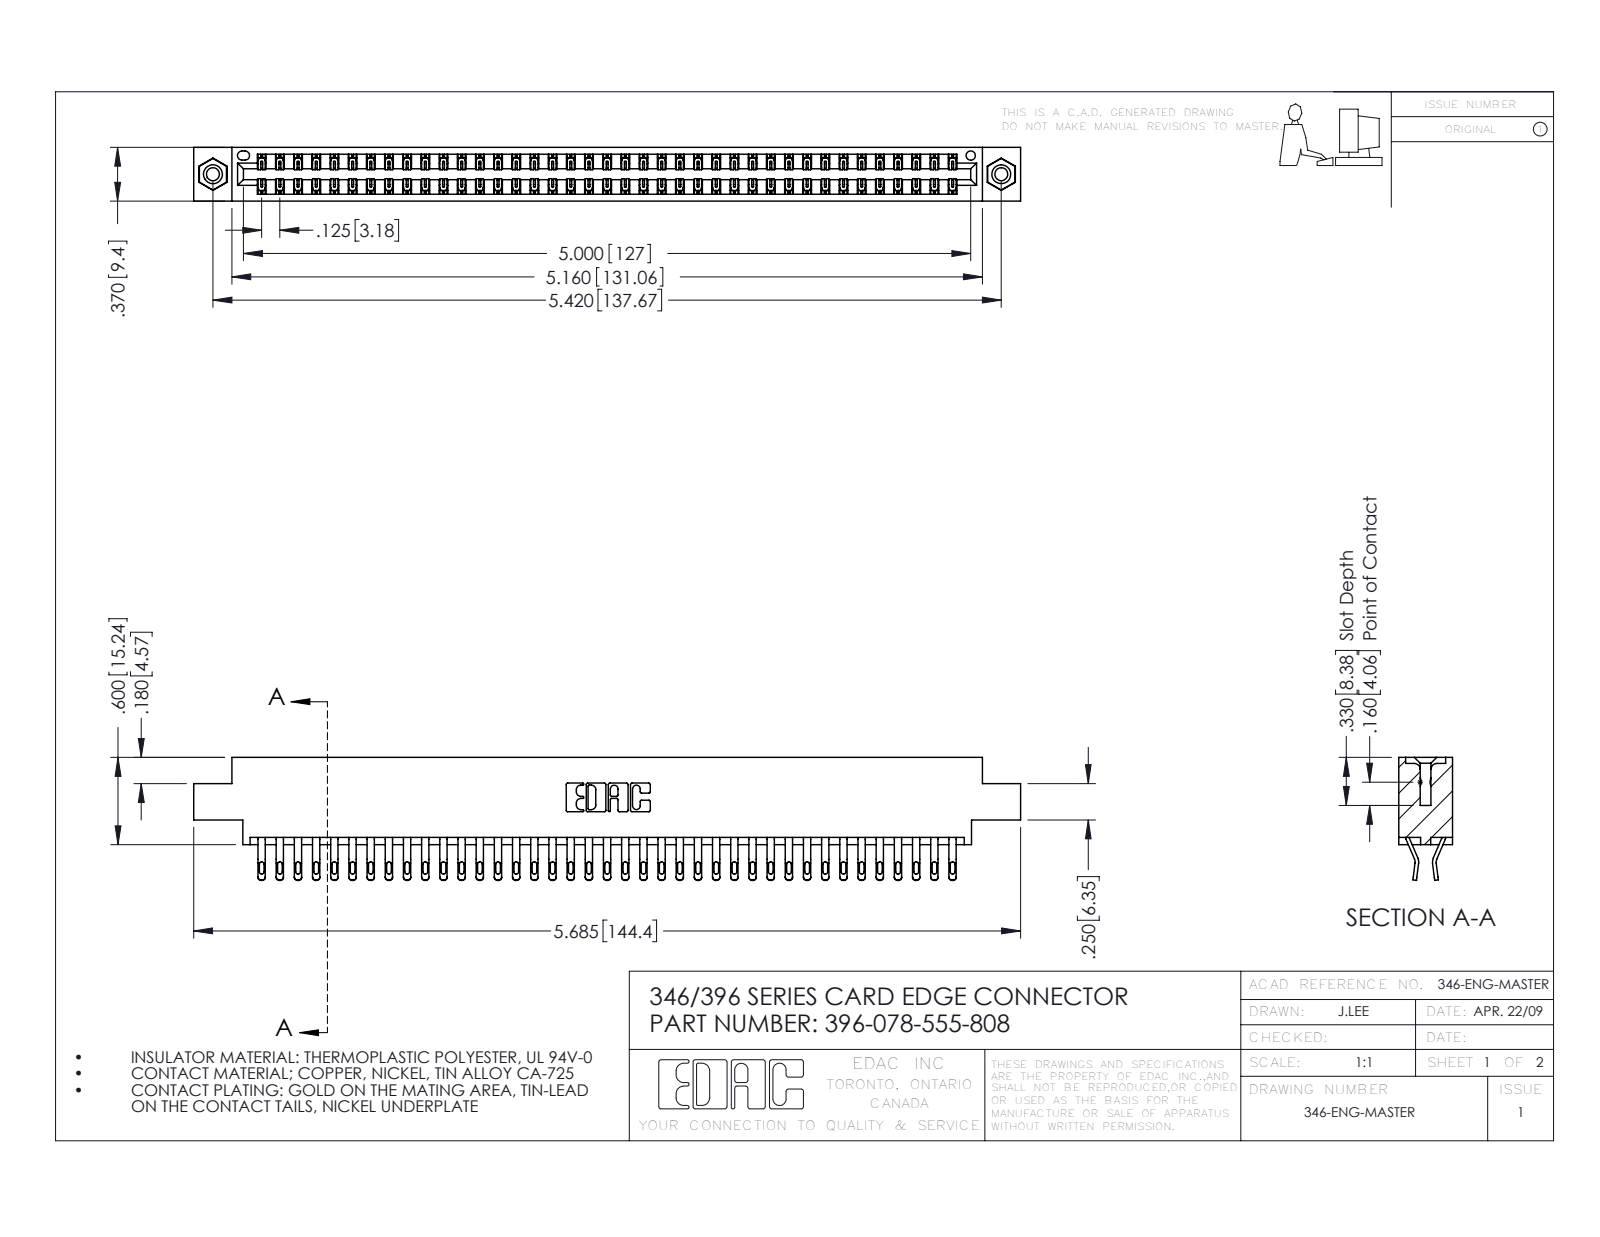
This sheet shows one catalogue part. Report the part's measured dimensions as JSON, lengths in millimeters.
{"part_name": "345-292-001_555 Tail; 345-250-001_345-250-003-102; 396-078-555-808; 346 Part_0.170 Offset - 0.156 Dia-TI", "step_written_by": "SolidWorks 2016 (CONFIG_CONTROL_DESIGN)", "units": "millimeters", "bodies": {"solids": 81, "faces": 4710, "planar": 2686, "cylindrical": 2008, "other": 16}, "overall_size": [144.4, 21.5, 9.4], "volume_mm3": 14100, "surface_area_mm2": 20370, "round_holes": [[2.3, 2], [3.2, 2], [4, 2], [1.6, 1]], "round_bosses_or_shafts": [[3.9, 2]], "partial_cylinders_radius": [[0.4, 156], [0.5, 156], [0.2, 117], [0.3, 22], [0.2, 6], [0.8, 6], [0.7, 3], [0.3, 2]], "face_to_face_distances": [1.2, 8.2, 9.4, 6.4, 0.6, 1.8, 7.6, 7, 5.6, 3.8], "hole_center_spacings": [6.2, 132.4, 137.7]}
